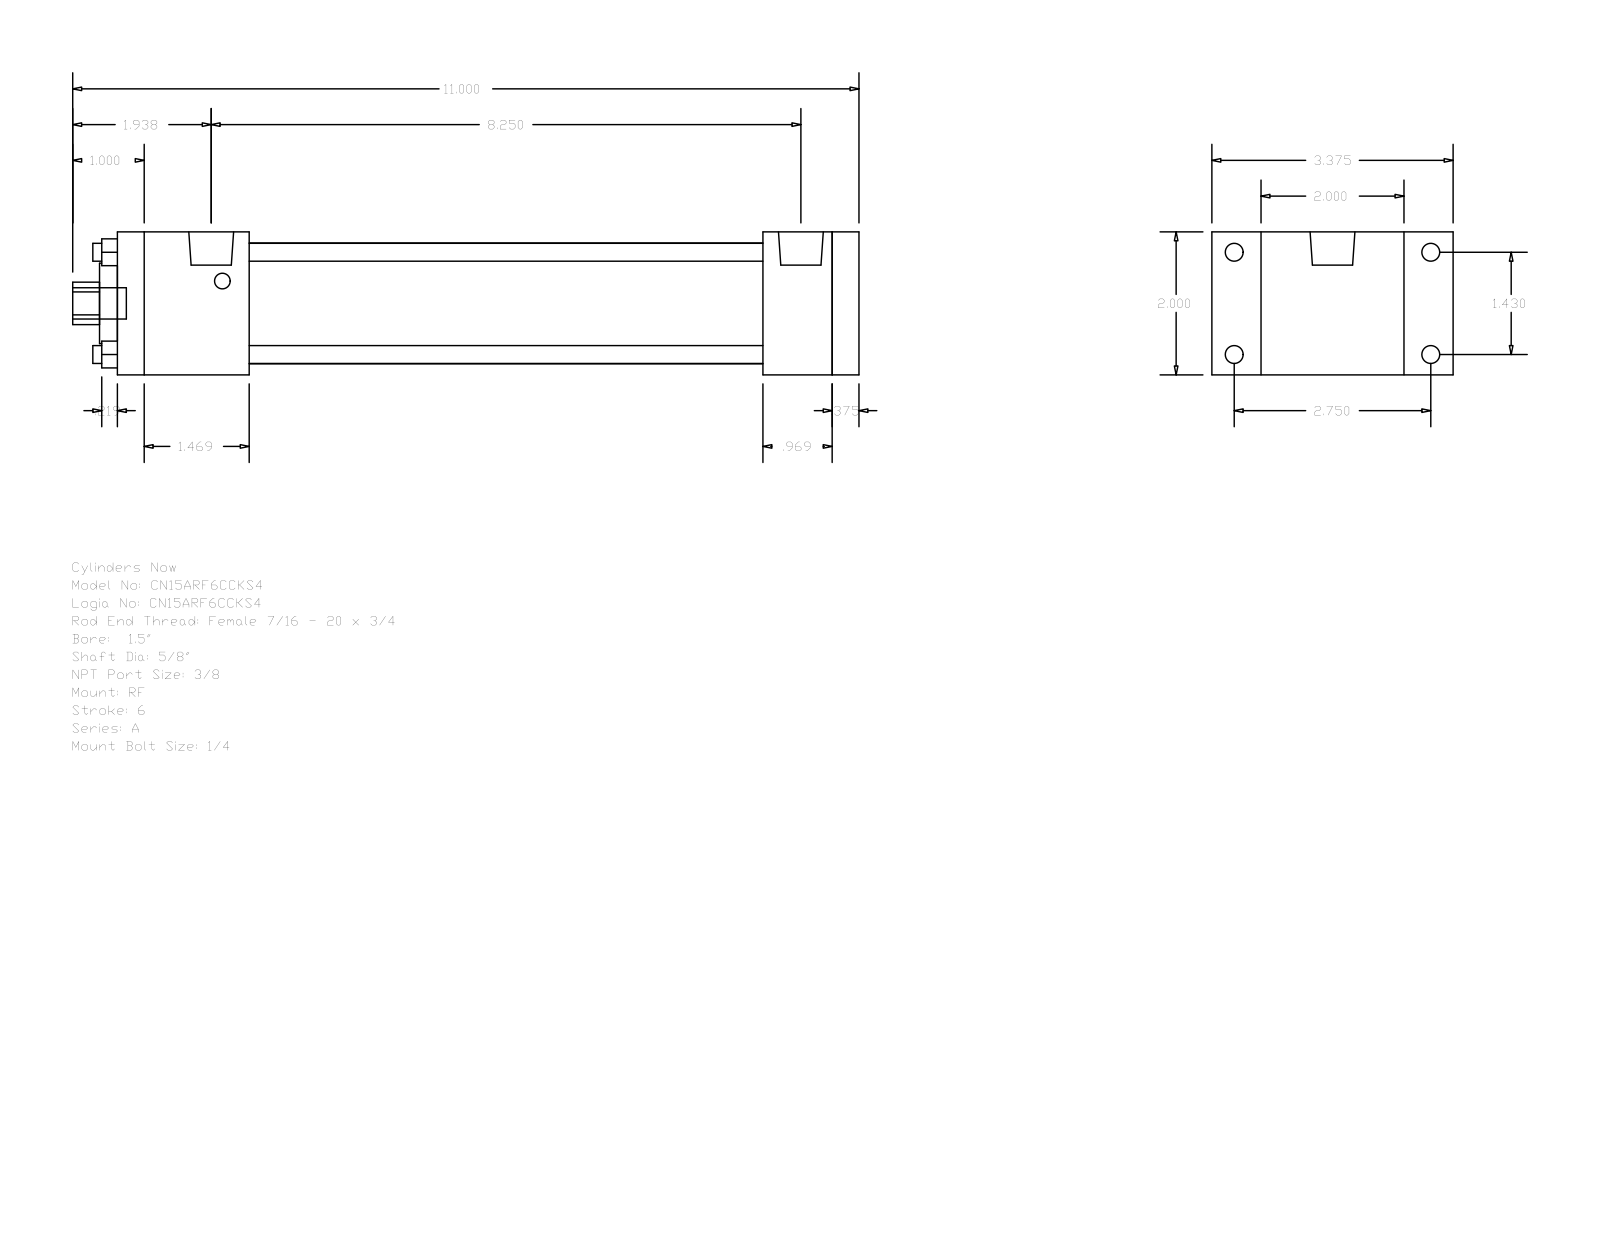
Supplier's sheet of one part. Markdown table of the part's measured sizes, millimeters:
| quantity | value |
| --- | --- |
| part name | A_RF__0150_0.625 |
| STEP written by | GSSL Pune (CONFIG_CONTROL_DESIGN) |
| units | millimeters |
| bodies | 0 solids, 92 faces (64 planar, 28 cylindrical, 0 other) |
| overall size | 279.4 × 85.72 × 50.8 |
| round holes (diameter × count) | 6.35 × 4, 15.88 × 1, 28.57 × 1, 42.93 × 1 |
| round bosses / shafts (diameter × count) | 6.35 × 4, 5.56 × 4, 15.93 × 2, 11.11 × 1 |
| partial cylindrical surfaces (radius × count) | 7.54 × 1 |
| main face-to-face distances | 50.8, 9.52, 254, 263.52, 229.39, 24.61, 34.13, 46.83, 182.56, 207.17 |
| hole center spacings | 25.68, 36.32, 51.36 |
